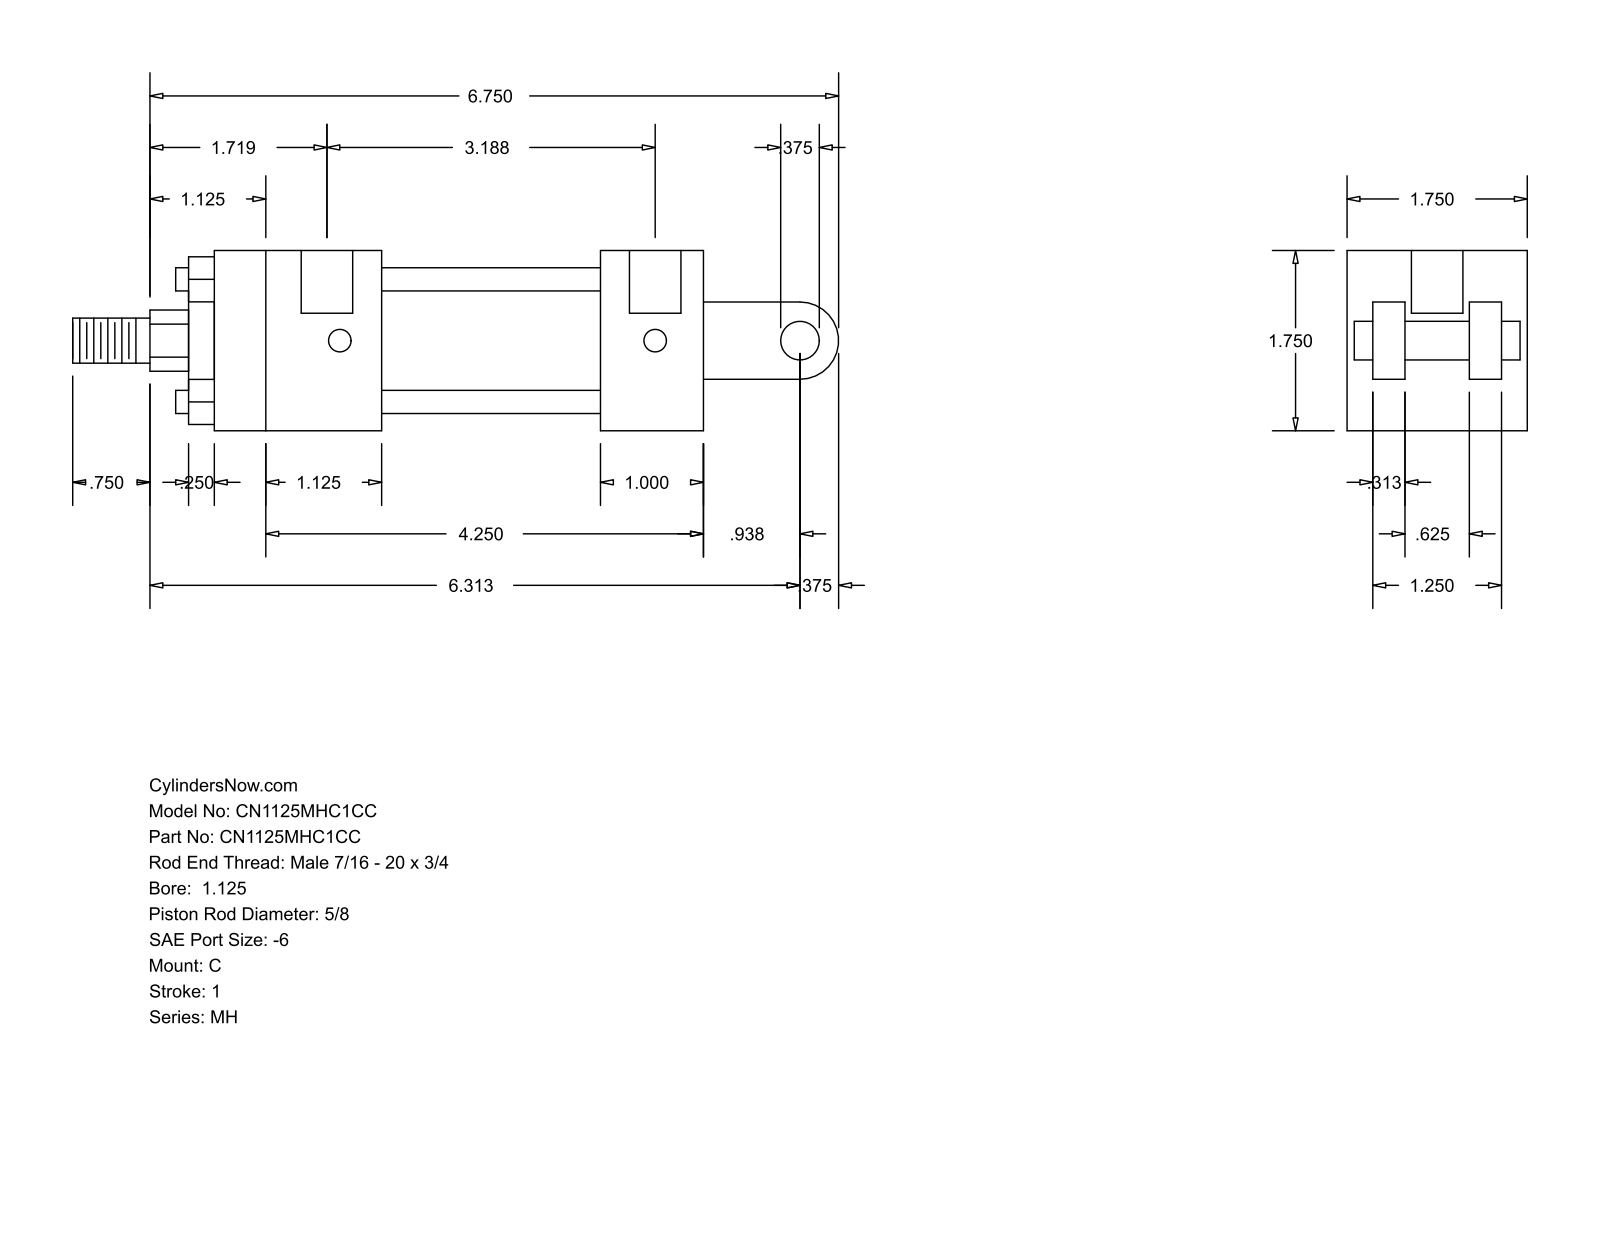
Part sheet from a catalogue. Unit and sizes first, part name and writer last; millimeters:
Units: millimetres
Overall size (bounding box): 188.91 × 44.45 × 44.45
Round holes (diameter × count): ⌀5.56 ×4, ⌀12.7 ×2
Round bosses / shafts (diameter × count): ⌀5.71 ×4, ⌀34.92 ×1, ⌀28.57 ×1, ⌀15.88 ×1, ⌀11.11 ×1, ⌀9.53 ×1
Partial cylindrical surfaces — rounded edges, fillets, slot ends (radius × count): R7.54 ×1, R9.53 ×1
Main face-to-face distances: 44.46, 6.35, 31.76, 14.29, 30.17, 38.11, 7.94, 23.82, 12.7, 41.27
Hole centre spacings: 77.79, 3.17, 80.96
Bodies: 0 solids, 99 faces (70 planar, 29 cylindrical, 0 other)
Part name (STEP PRODUCT): MH_C__0112_0.625
STEP written by: GSSL Pune (CONFIG_CONTROL_DESIGN)
